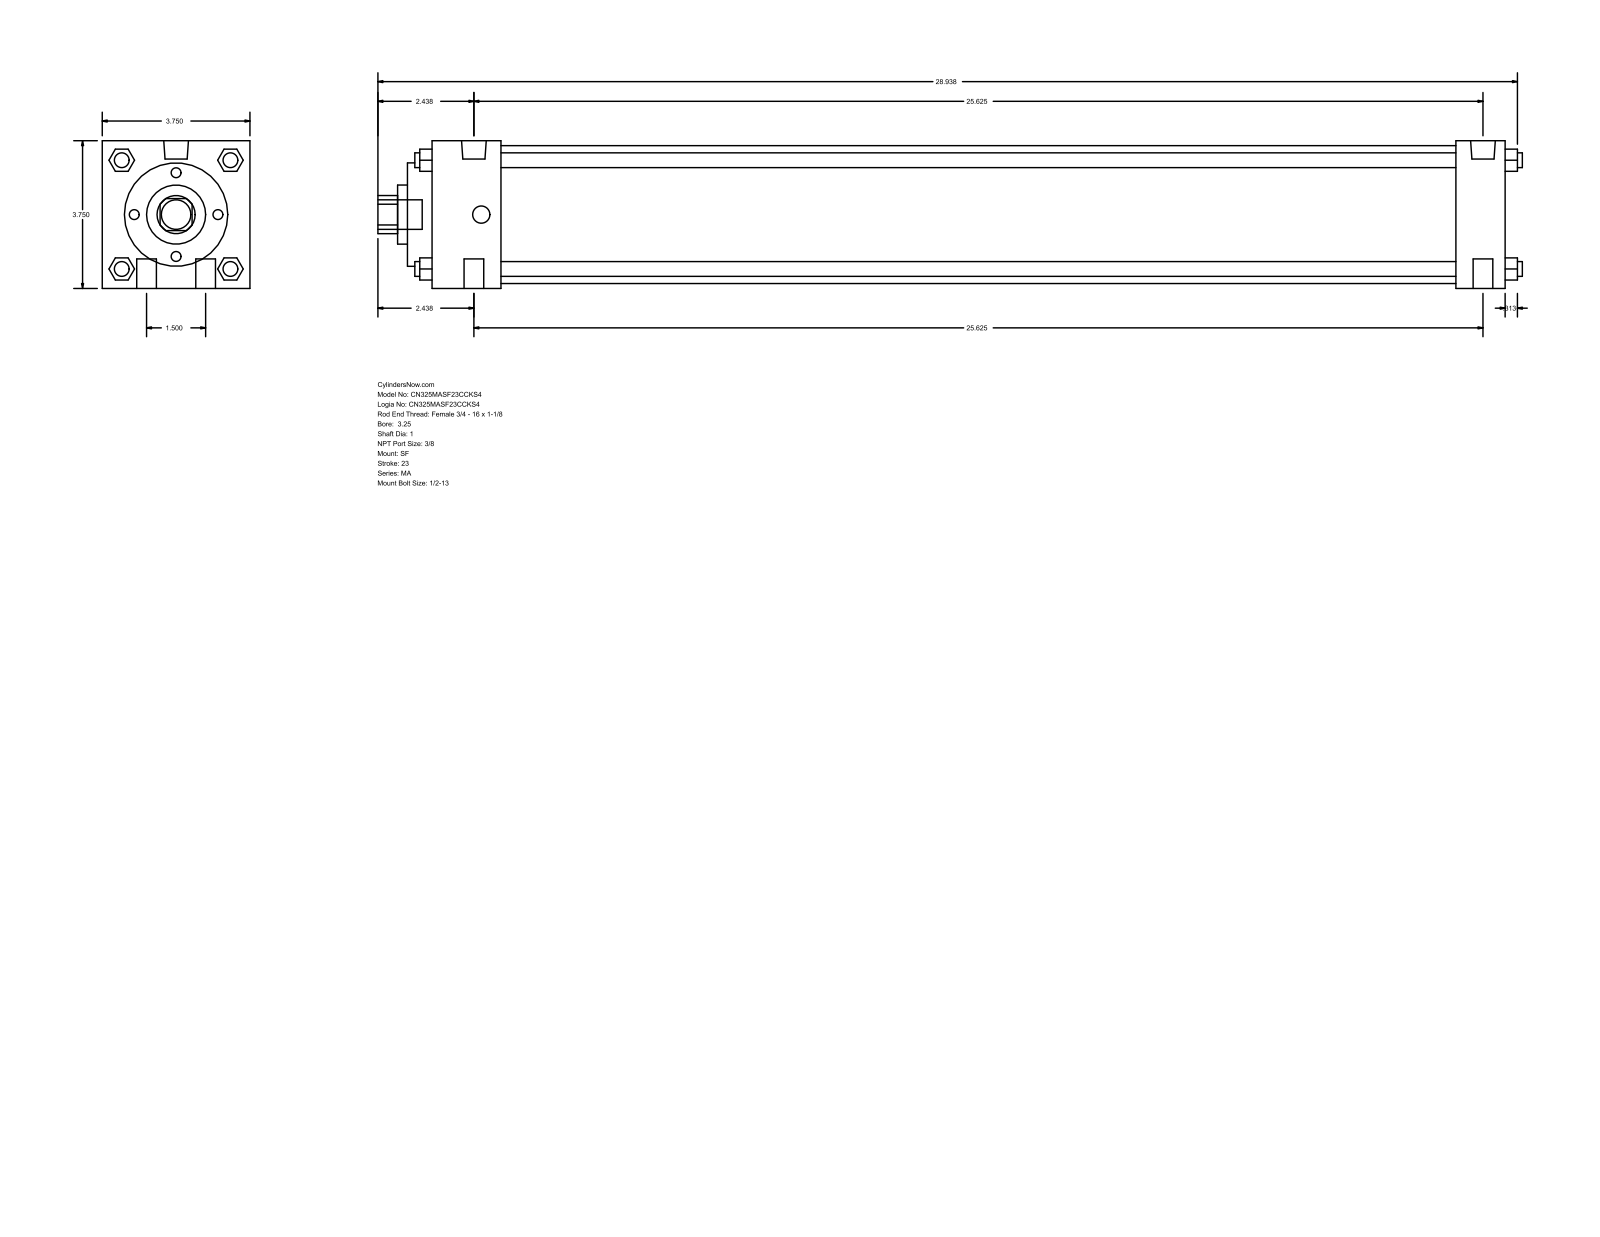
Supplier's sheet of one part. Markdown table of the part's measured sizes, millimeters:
| quantity | value |
| --- | --- |
| part name | MA_SF__0325_1 |
| STEP written by | GSSL Pune (CONFIG_CONTROL_DESIGN) |
| units | millimeters |
| bodies | 0 solids, 126 faces (95 planar, 31 cylindrical, 0 other) |
| overall size | 738.19 × 95.25 × 95.25 |
| round holes (diameter × count) | 25.4 × 1, 38.1 × 1, 66.67 × 1, 88.9 × 1 |
| round bosses / shafts (diameter × count) | 12.7 × 4, 9.53 × 4, 15.93 × 2, 11.11 × 2, 19.05 × 1 |
| partial cylindrical surfaces (radius × count) | 12.29 × 1 |
| main face-to-face distances | 95.24, 692.16, 15.87, 660.41, 31.75, 44.46, 615.95, 647.7, 60.33, 676.28 |
